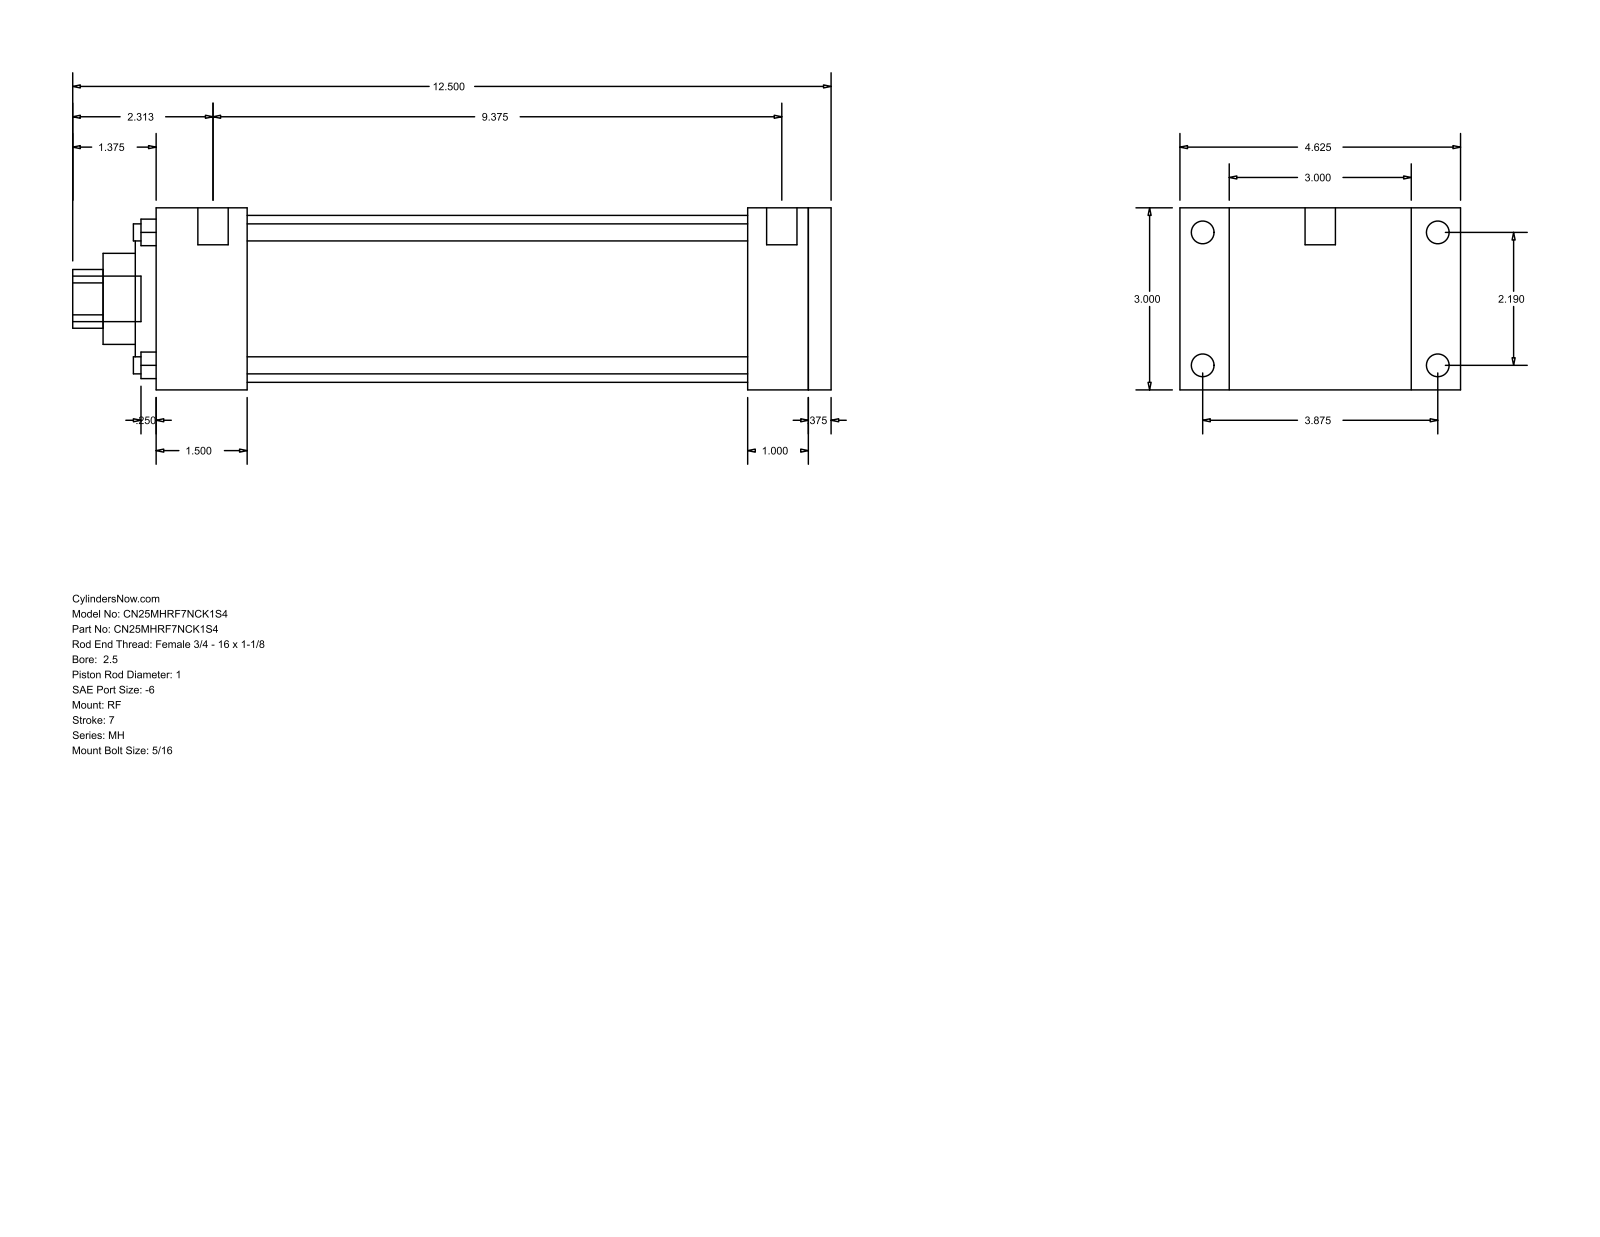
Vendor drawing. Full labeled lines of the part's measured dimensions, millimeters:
Part name (STEP PRODUCT): MH_RF__0250_1
STEP written by: GSSL Pune (CONFIG_CONTROL_DESIGN)
Units: millimetres
Bodies: 0 solids, 94 faces (65 planar, 29 cylindrical, 0 other)
Overall size (bounding box): 317.5 × 117.47 × 76.2
Round holes (diameter × count): ⌀7.14 ×4, ⌀25.4 ×1, ⌀38.1 ×1, ⌀60.33 ×1, ⌀69.85 ×1
Round bosses / shafts (diameter × count): ⌀9.53 ×4, ⌀5.56 ×4, ⌀12.7 ×2, ⌀19.05 ×1
Partial cylindrical surfaces — rounded edges, fillets, slot ends (radius × count): R12.29 ×1
Main face-to-face distances: 76.2, 9.52, 282.58, 273.06, 247.65, 25.41, 34.93, 38.11, 209.54, 234.95
Hole centre spacings: 39.33, 55.62, 78.66
